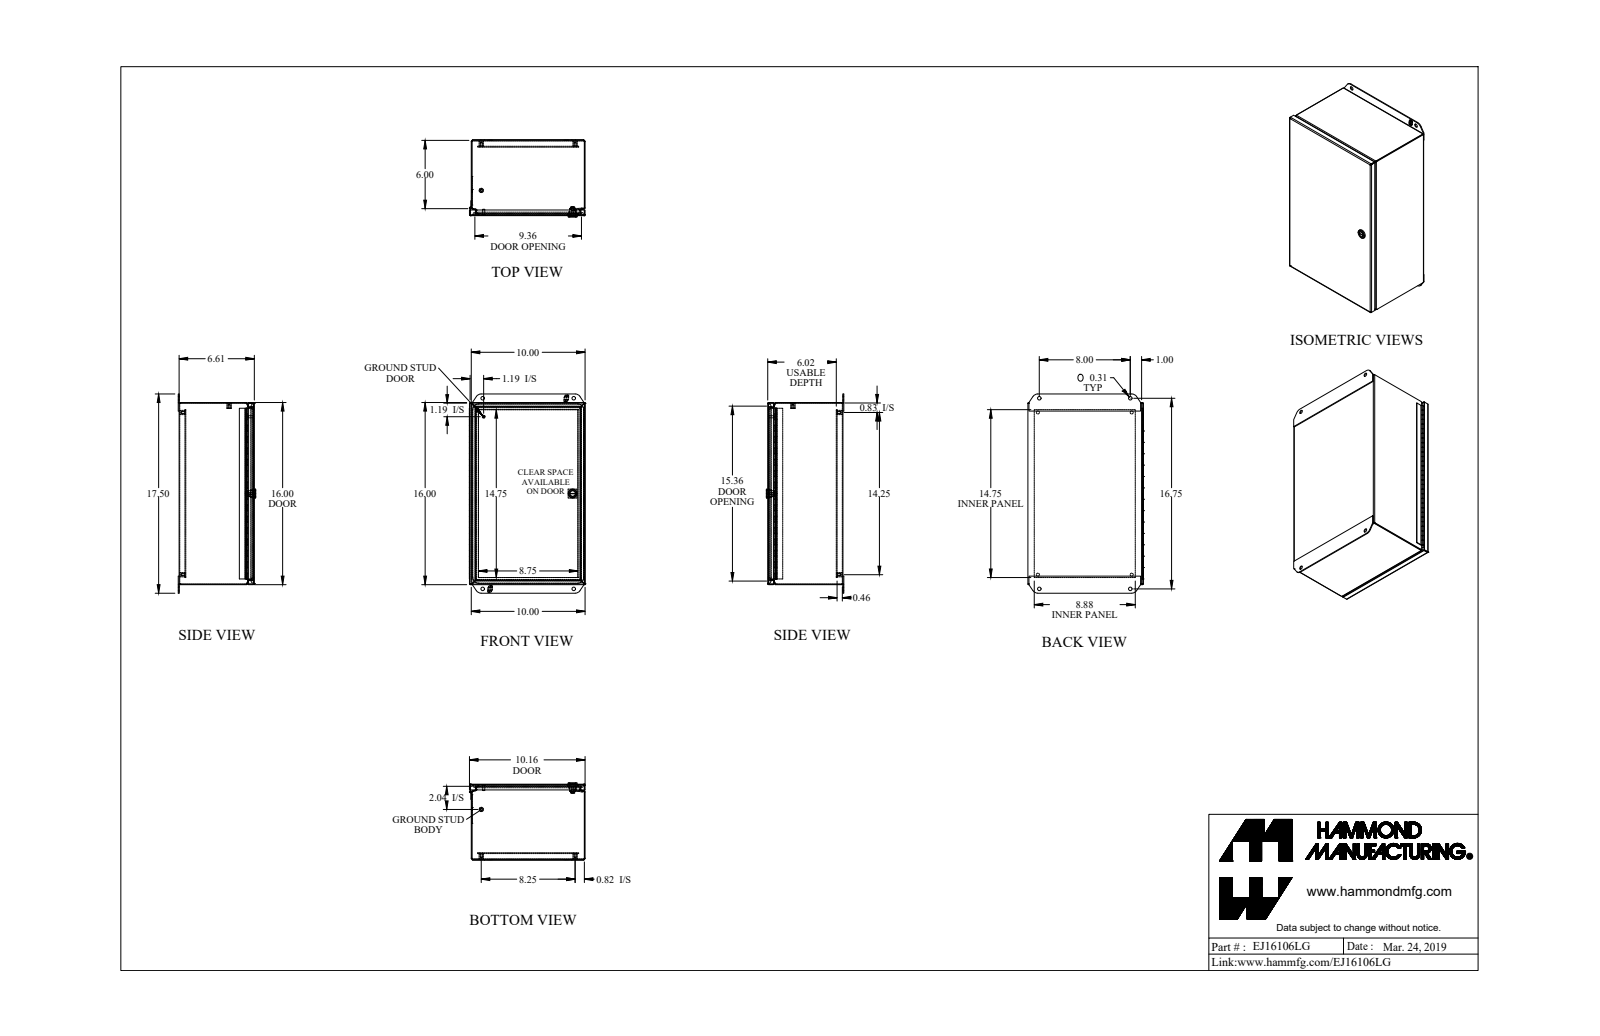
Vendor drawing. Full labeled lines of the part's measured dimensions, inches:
Part name (STEP PRODUCT): EJ16106LG_Default
STEP written by: SolidWorks 2019 (CONFIG_CONTROL_DESIGN)
Units: inches
Bodies: 16 solids, 771 faces (425 planar, 254 cylindrical, 92 other)
Overall size (bounding box): 17.5 × 10.165 × 6.805
Volume: 56.45 in³ · Surface area: 1 870 in²
Round holes (diameter × count): ⌀0.156 ×5, ⌀0.265 ×4, ⌀0.313 ×4, ⌀0.05 ×1, ⌀0.516 ×1
Round bosses / shafts (diameter × count): ⌀0.375 ×5, ⌀0.788 ×1, ⌀0.535 ×1, ⌀0.496 ×1, ⌀0.435 ×1, ⌀0.25 ×1, ⌀0.188 ×1, ⌀0.1 ×1
Partial cylindrical surfaces — rounded edges, fillets, slot ends (radius × count): R0.029 ×16, R0.086 ×16, R0.281 ×10, R0.25 ×4, R0.499 ×4, R0.5 ×4, R0.06 ×2, R0.539 ×2
Main face-to-face distances: 0.057, 6.554, 9.943, 0.072, 0.589, 6.611, 6.497, 0.46, 0.517, 6.094
Hole centre spacings: 1.257, 15.5, 17.5, 14.25, 8.22, 16.465, 7.128, 8
